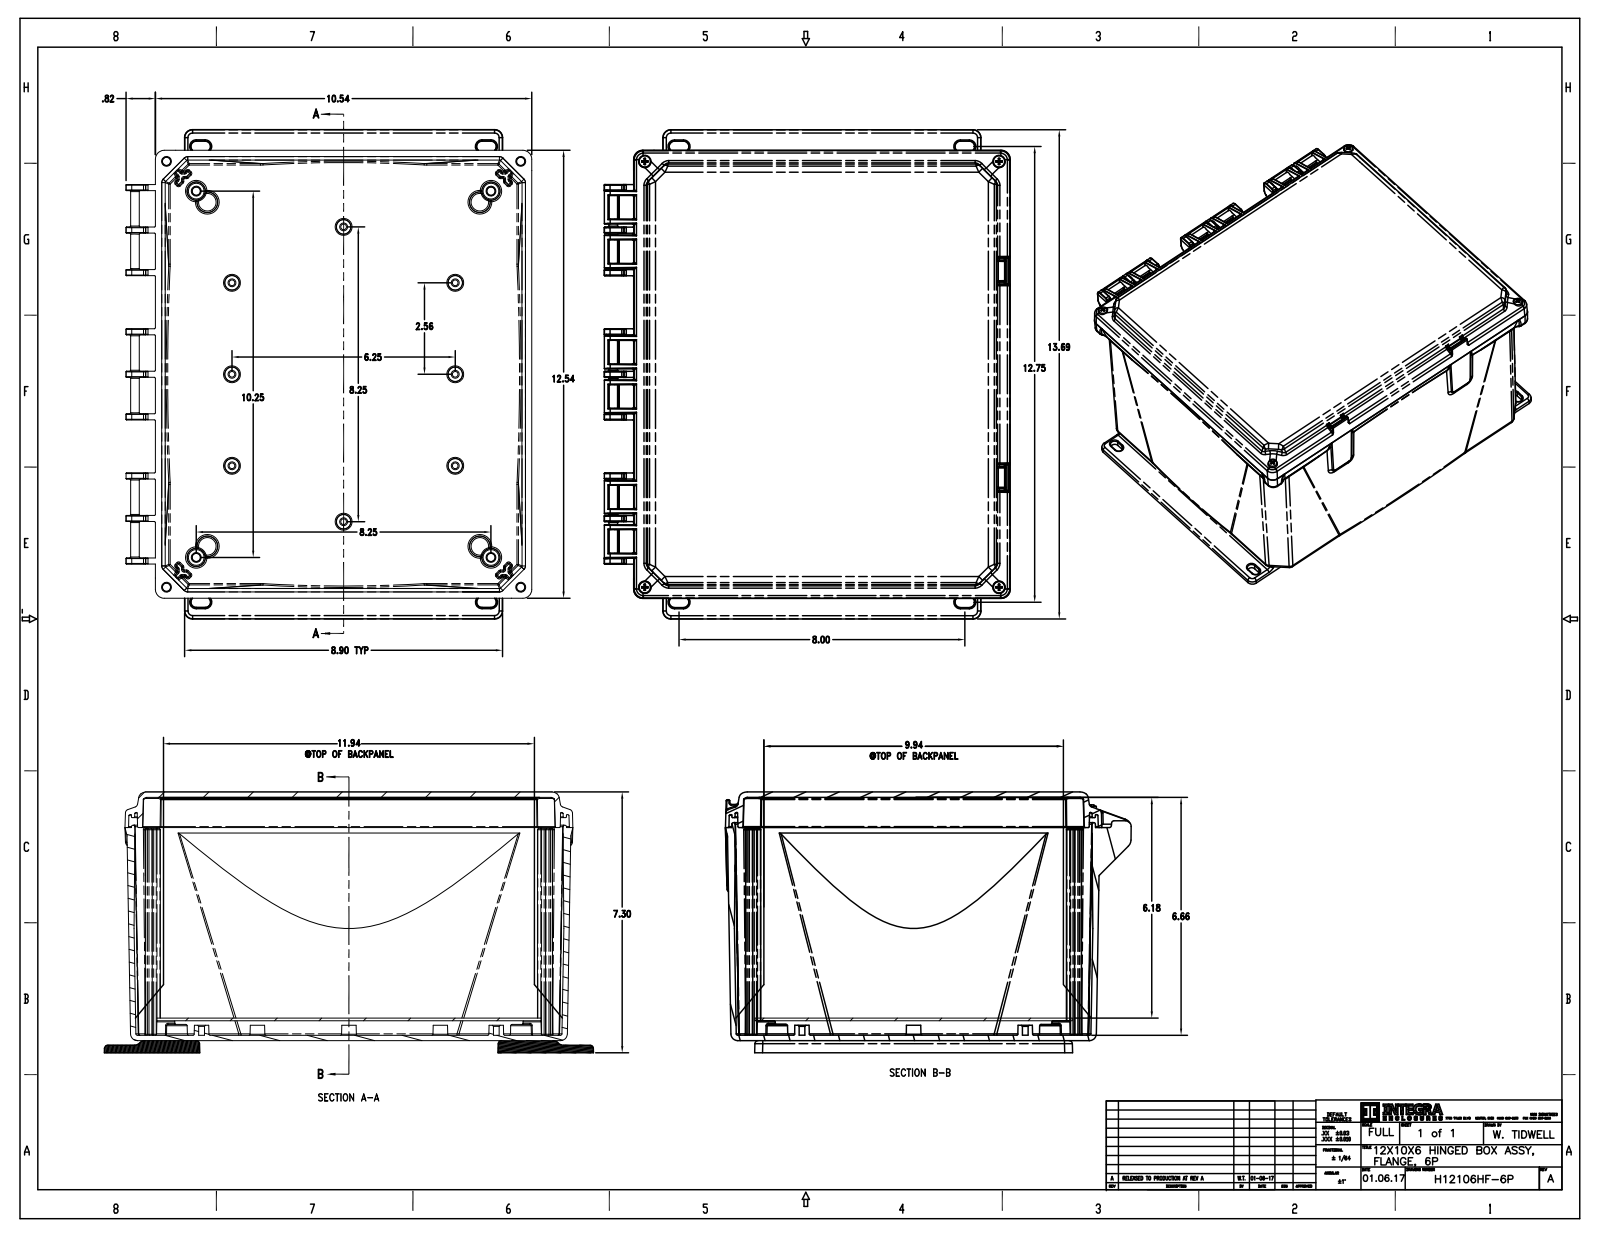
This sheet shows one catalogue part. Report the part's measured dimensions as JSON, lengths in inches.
{"part_name": "H12106BH; 9912525-80-10; 9912521-80-10; H12106BH_ASM (+5 more)", "step_written_by": "CREO PARAMETRIC BY PTC INC, 2016050 (CONFIG_CONTROL_DESIGN)", "units": "inches", "bodies": {"solids": 24, "faces": 4447, "planar": 1047, "cylindrical": 1790, "other": 1610}, "overall_size": [13.69, 11.359, 7.3], "volume_in3": 99.72, "surface_area_in2": 1357, "round_holes": [[0.16, 8], [0.19, 8], [0.201, 4]], "round_bosses_or_shafts": [[0.25, 12], [0.3, 8], [0.298, 8], [0.29, 8], [0.26, 8], [0.258, 8], [0.375, 4], [0.372, 4]], "partial_cylinders_radius": [[0.03, 446], [0.02, 153], [0.015, 91], [0.005, 48], [0.04, 39], [0.09, 36], [0.1, 28], [0.01, 26]], "face_to_face_distances": [0.15, 0.49, 0.12, 5.81, 5.96, 6.08, 0.27, 0.392, 0.34, 0.098], "hole_center_spacings": [0.438, 1.178, 1.616, 2.358, 2.56, 2.753, 3.495, 3.861]}
